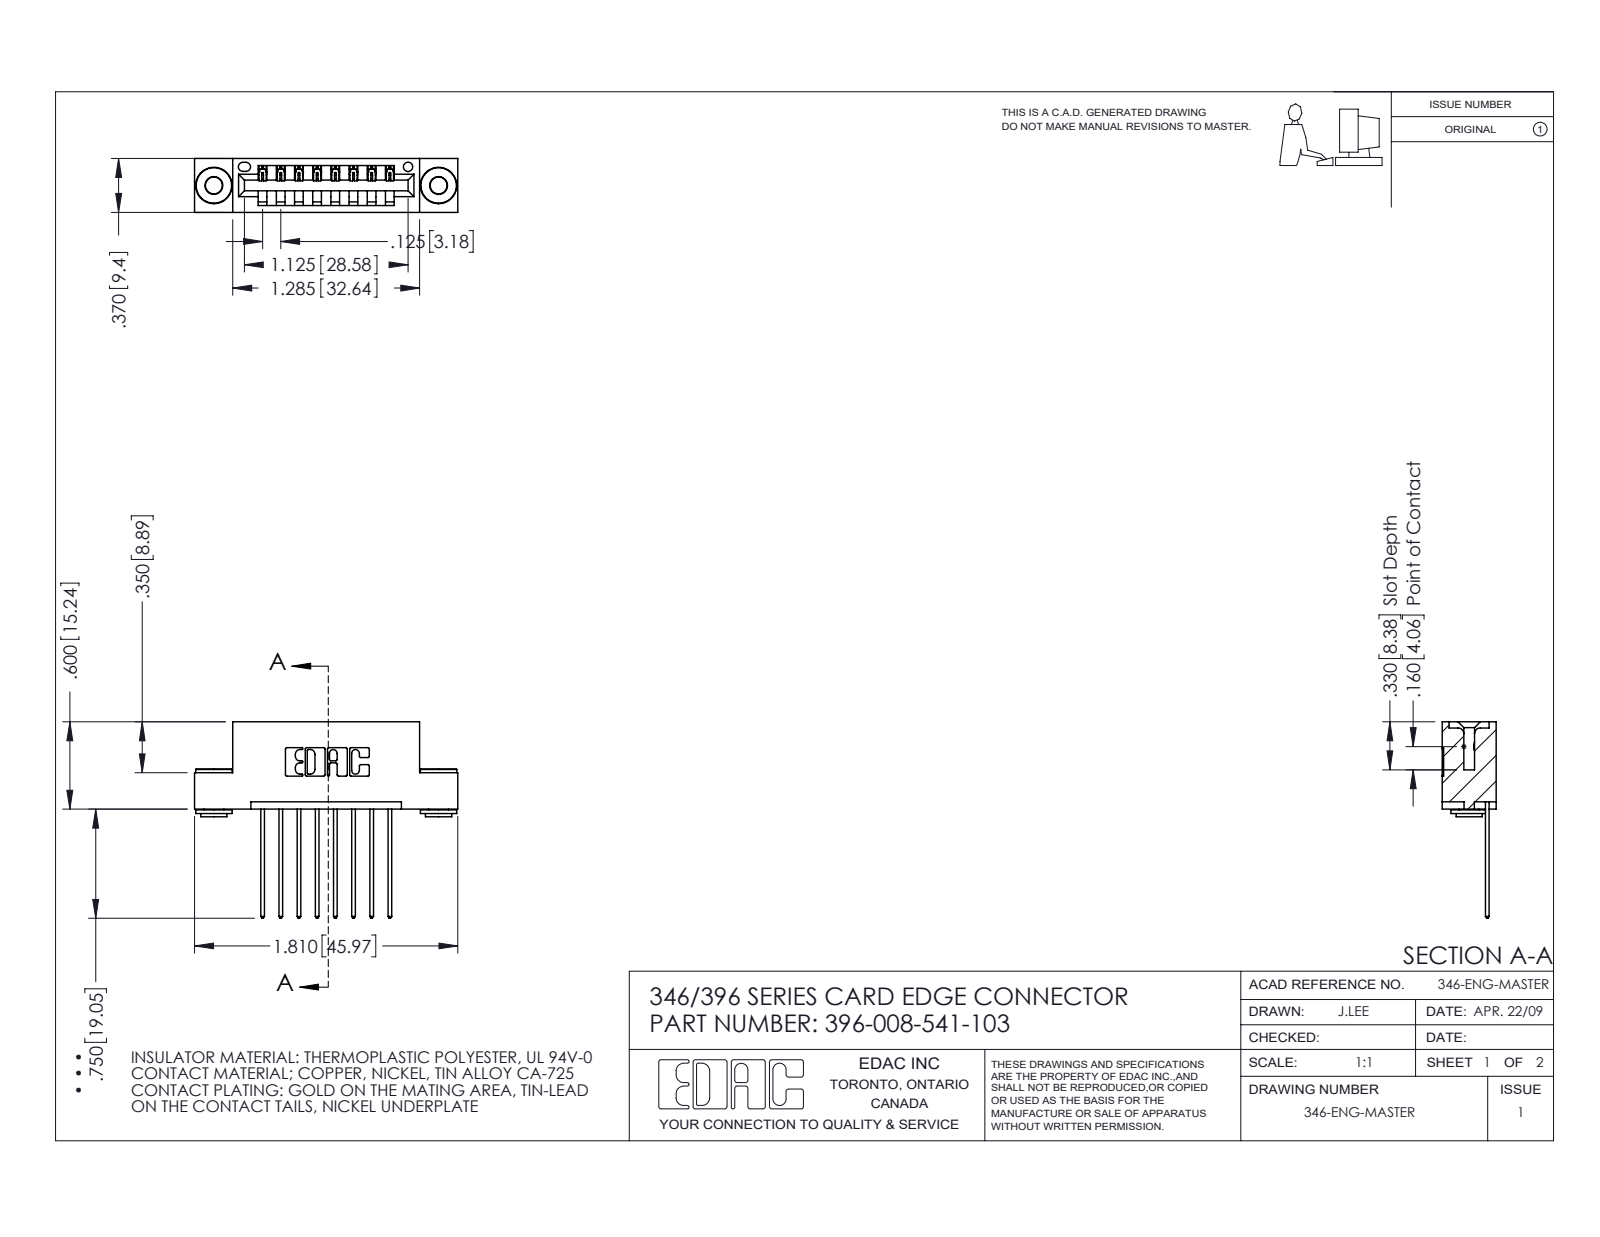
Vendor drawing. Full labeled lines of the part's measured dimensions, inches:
Part name (STEP PRODUCT): 396-008-541-103; 345-250-002_345-250-002-102; 345-292-001_345-293-141; 346 Part_Flush Mounting Lugs - 0.156 Dia-TH
STEP written by: SolidWorks 2016 (CONFIG_CONTROL_DESIGN)
Units: inches
Bodies: 11 solids, 624 faces (406 planar, 210 cylindrical, 8 other)
Overall size (bounding box): 1.81 × 1.35 × 0.37
Volume: 0.257 in³ · Surface area: 8.176 in²
Round holes (diameter × count): ⌀0.116 ×2, ⌀0.156 ×2, ⌀0.064 ×1
Round bosses / shafts (diameter × count): ⌀0.25 ×2, ⌀0.18 ×2, ⌀0.136 ×2
Partial cylindrical surfaces — rounded edges, fillets, slot ends (radius × count): R0.01 ×22, R0.006 ×16, R0.01 ×16, R0.007 ×6, R0.031 ×6, R0.026 ×3, R0.031 ×2, R0.04 ×2
Main face-to-face distances: 0.25, 0.048, 0.322, 0.37, 0.025, 0.072, 0.298, 0.5, 0.148, 0.222
Hole centre spacings: 0.246, 1.341, 1.545
